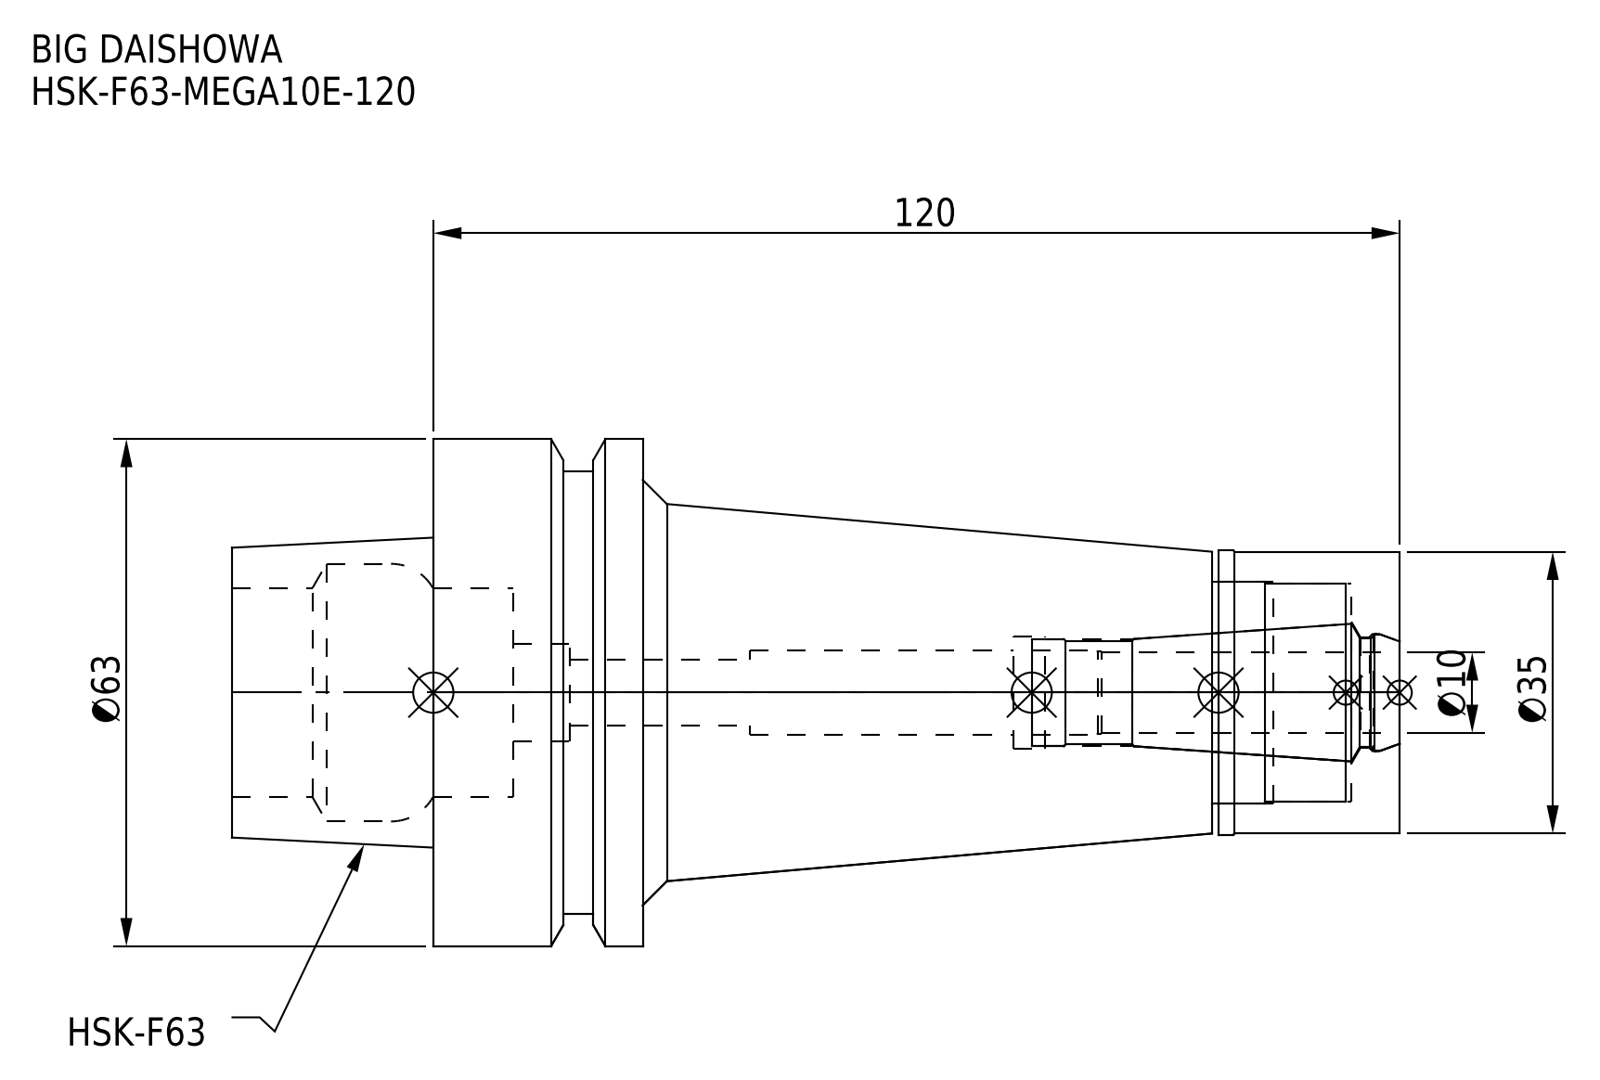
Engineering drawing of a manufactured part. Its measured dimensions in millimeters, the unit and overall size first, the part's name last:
Units: millimetres
Overall size (bounding box): 145 × 63 × 63
Round holes (diameter × count): ⌀8.25 ×1, ⌀10.4 ×1, ⌀12 ×1, ⌀13.3 ×1, ⌀13.8 ×1, ⌀13.9 ×1, ⌀14.7 ×1, ⌀26 ×1, ⌀27 ×1, ⌀27.5 ×1, ⌀32 ×1
Round bosses / shafts (diameter × count): ⌀63 ×1, ⌀55 ×1, ⌀35.3 ×1, ⌀35 ×1
Main face-to-face distances: 26, 94, 120, 145, 51, 25, 110.05, 16.05, 9.95, 34.95
Volume: 187 439 mm³ · Surface area: 37 479 mm²
Bodies: 2 solids, 81 faces (17 planar, 40 cylindrical, 24 other)
Part name (STEP PRODUCT): HSK-F63-MEGA10E-120; HSK-F63-MEGA10E-120-100-FreeParts; HF63ME10120-100_ASM.stp; MEN10_1.stp (+3 more)
STEP written by: SolidWorks 2019 (CONFIG_CONTROL_DESIGN)
